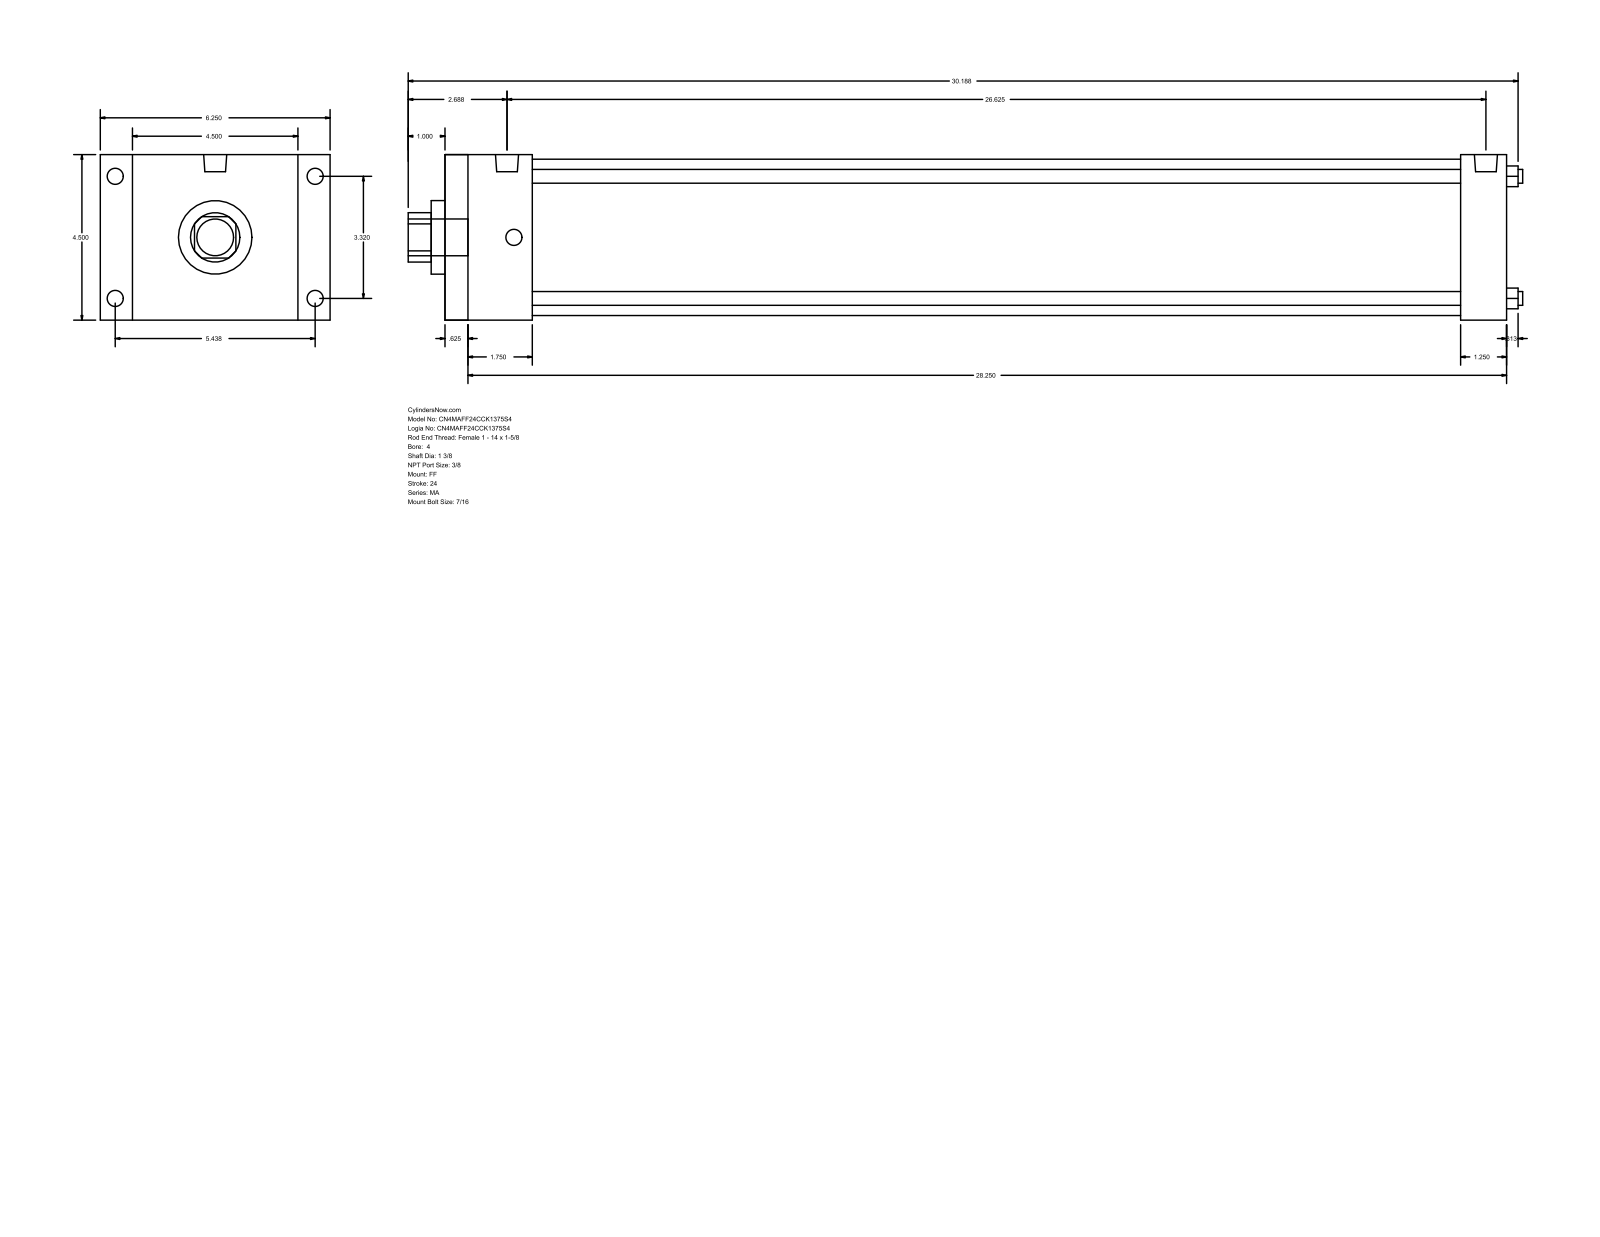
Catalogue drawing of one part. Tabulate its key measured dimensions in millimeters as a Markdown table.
| quantity | value |
| --- | --- |
| part name | MA_FF__0400_1.375 |
| STEP written by | GSSL Pune (CONFIG_CONTROL_DESIGN) |
| units | millimeters |
| bodies | 0 solids, 92 faces (64 planar, 28 cylindrical, 0 other) |
| overall size | 769.94 × 158.75 × 114.3 |
| round holes (diameter × count) | 9.53 × 4, 34.92 × 1, 50.8 × 1, 107.95 × 1 |
| round bosses / shafts (diameter × count) | 11.11 × 8, 15.93 × 2, 25.4 × 1 |
| partial cylindrical surfaces (radius × count) | 17.06 × 1 |
| main face-to-face distances | 114.3, 733.43, 15.87, 717.56, 22.23, 136.53, 701.68, 685.81, 31.75, 60.32 |
| hole center spacings | 59.62, 84.32, 119.25 |
